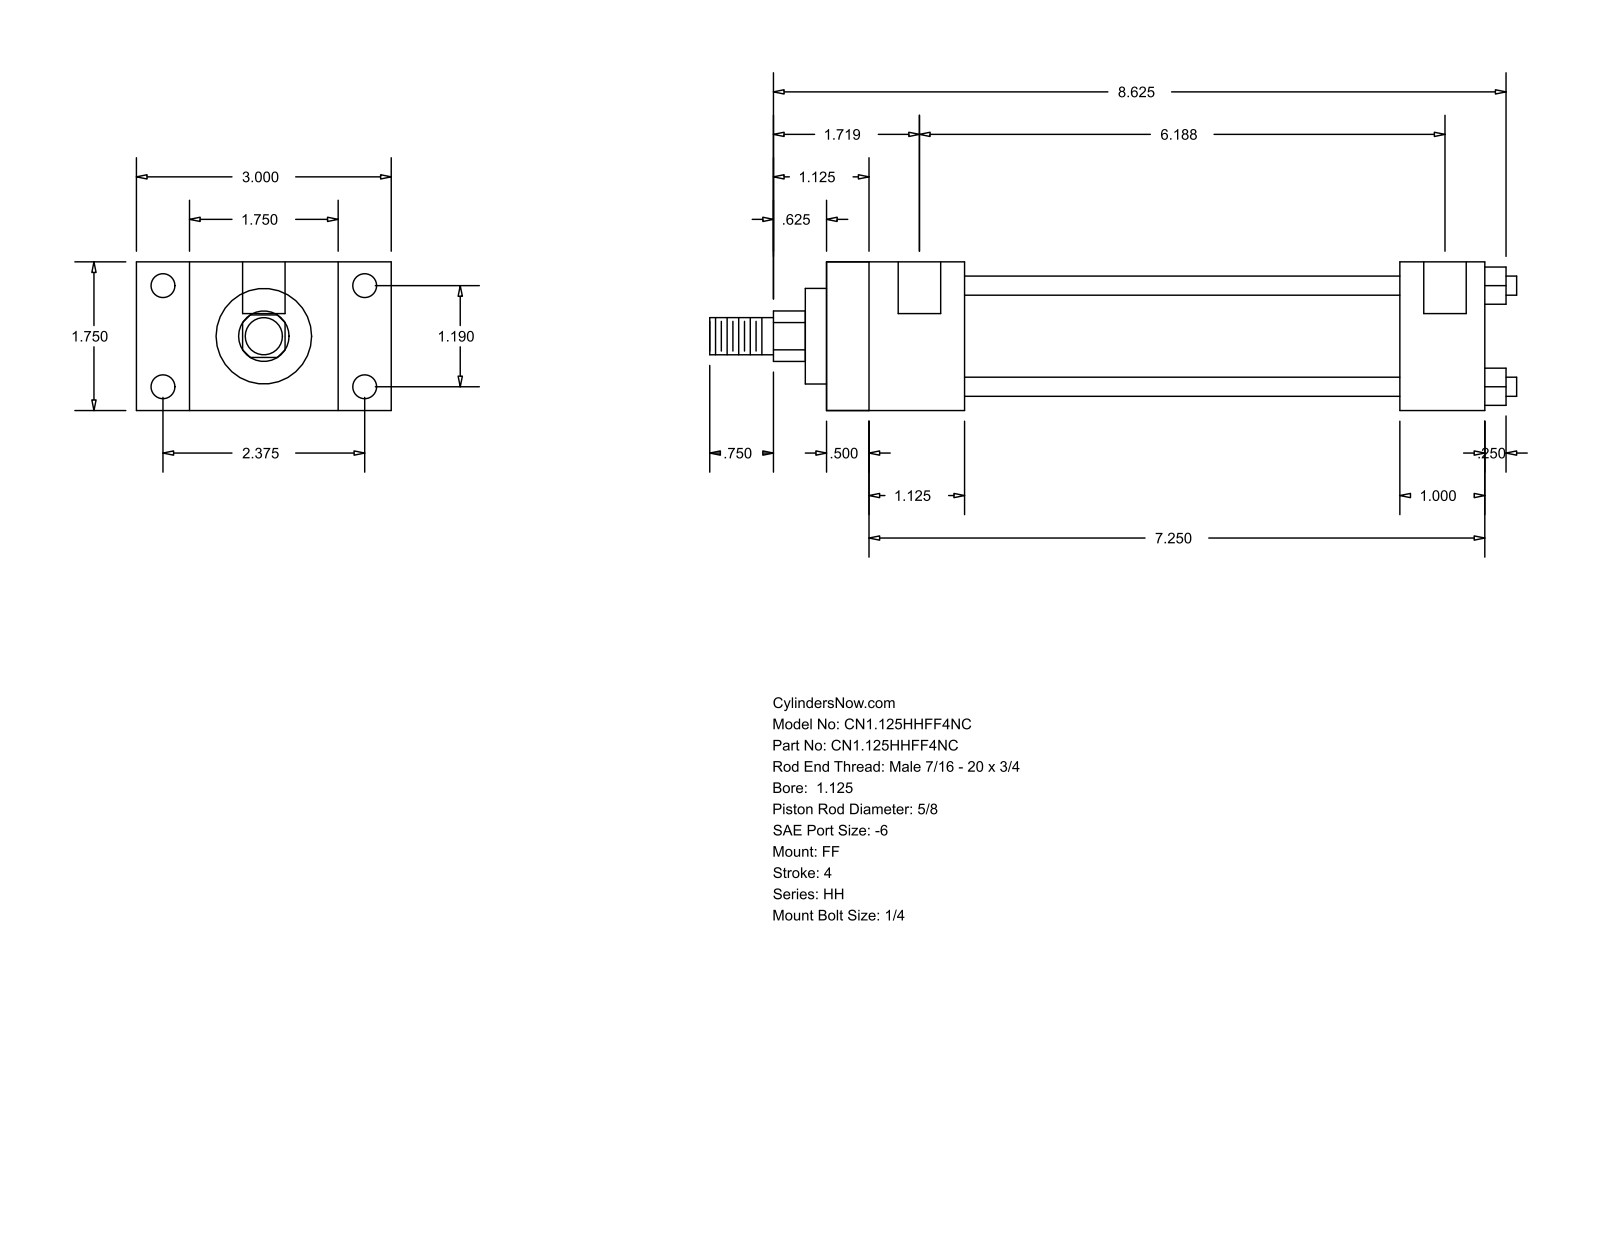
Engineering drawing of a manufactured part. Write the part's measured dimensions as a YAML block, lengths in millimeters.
part_name: "HH_FF__0112_0.625"
step_written_by: "GSSL Pune (CONFIG_CONTROL_DESIGN)"
units: millimeters
bodies: {solids: 0, faces: 92, planar: 64, cylindrical: 28, other: 0}
overall_size: [241.3, 76.2, 44.45]
round_holes:
  - {diameter: 5.56, count: 4}
  - {diameter: 7.14, count: 4}
  - {diameter: 12.7, count: 2}
round_bosses_or_shafts:
  - {diameter: 5.71, count: 4}
  - {diameter: 34.92, count: 1}
  - {diameter: 28.57, count: 1}
  - {diameter: 15.88, count: 1}
  - {diameter: 11.11, count: 1}
partial_cylinders:
  - {radius: 7.54, count: 1}
face_to_face_distances: [44.46, 196.84, 15.87, 12.69, 184.15, 28.58, 60.33, 25.4, 41.27, 171.44]
hole_center_spacings: [30.22, 60.32, 67.47, 153.99, 3.17, 157.16]
